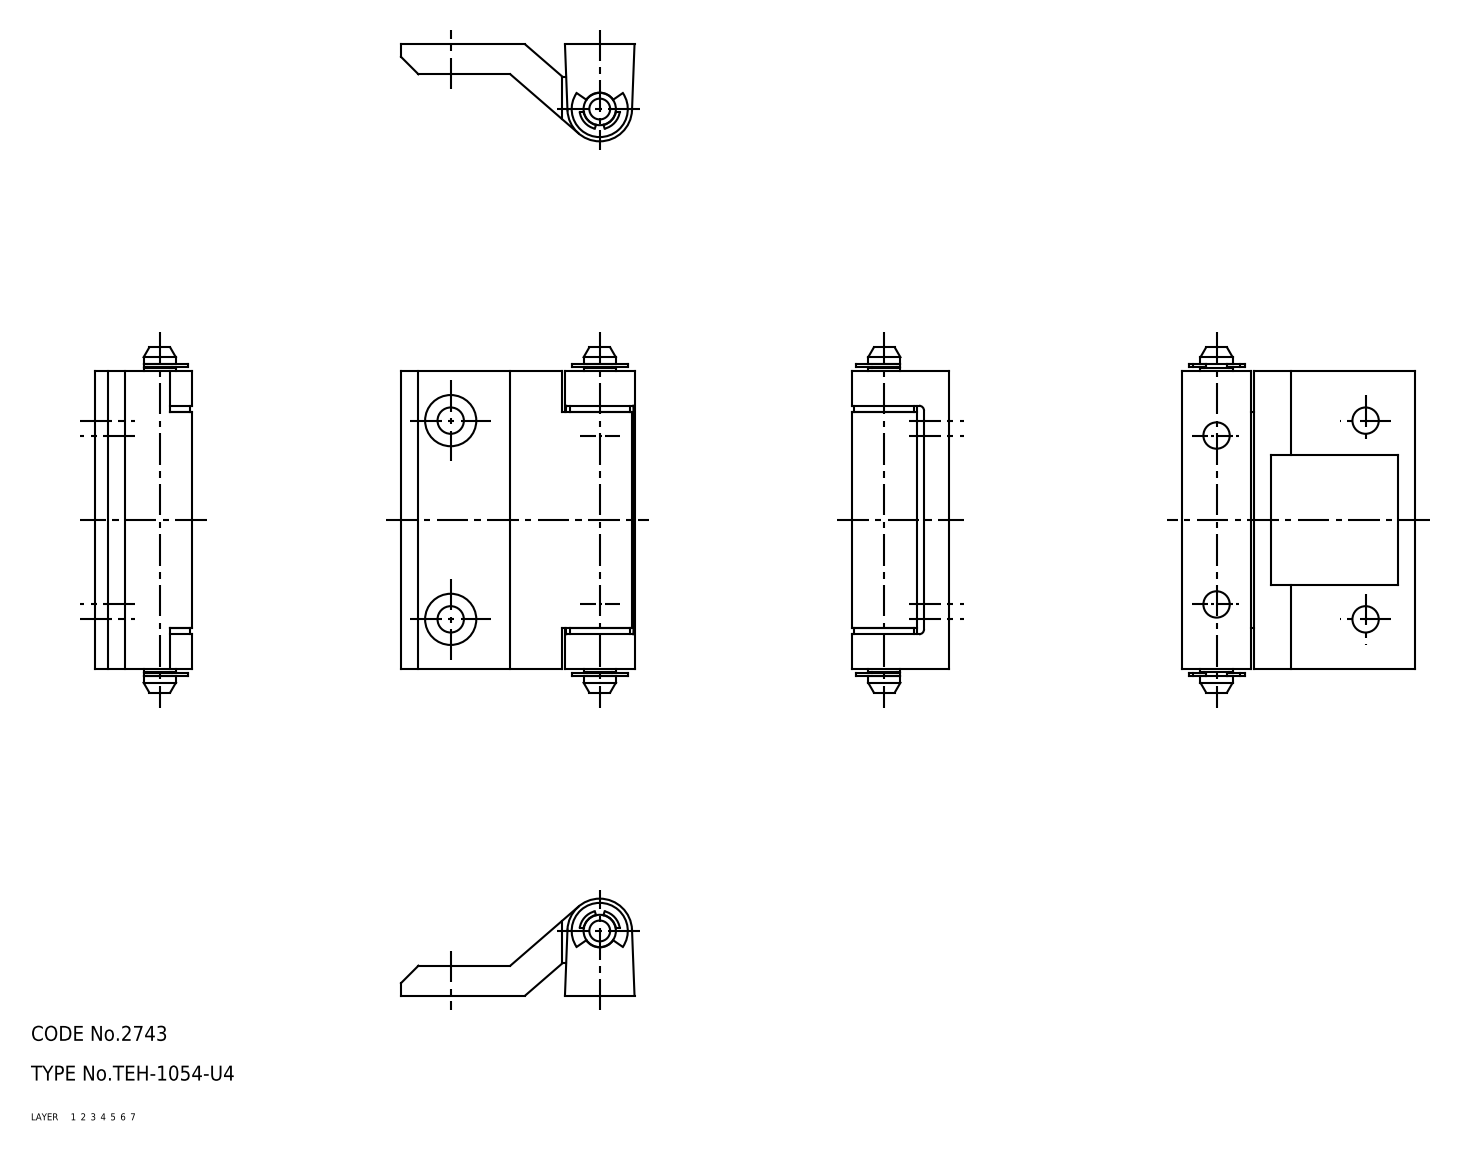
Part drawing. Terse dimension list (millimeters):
name: bushing; retainer; shaft; hinge pieces_B (+2 more)
written by: CADfix (AUTOMOTIVE_DESIGN)
unit: mm
bodies: 7 solids, 124 faces (0 planar, 0 cylindrical, 124 other)
size: 69.5 × 47 × 19.5
volume: 22 973 mm³; area: 14 460 mm²
